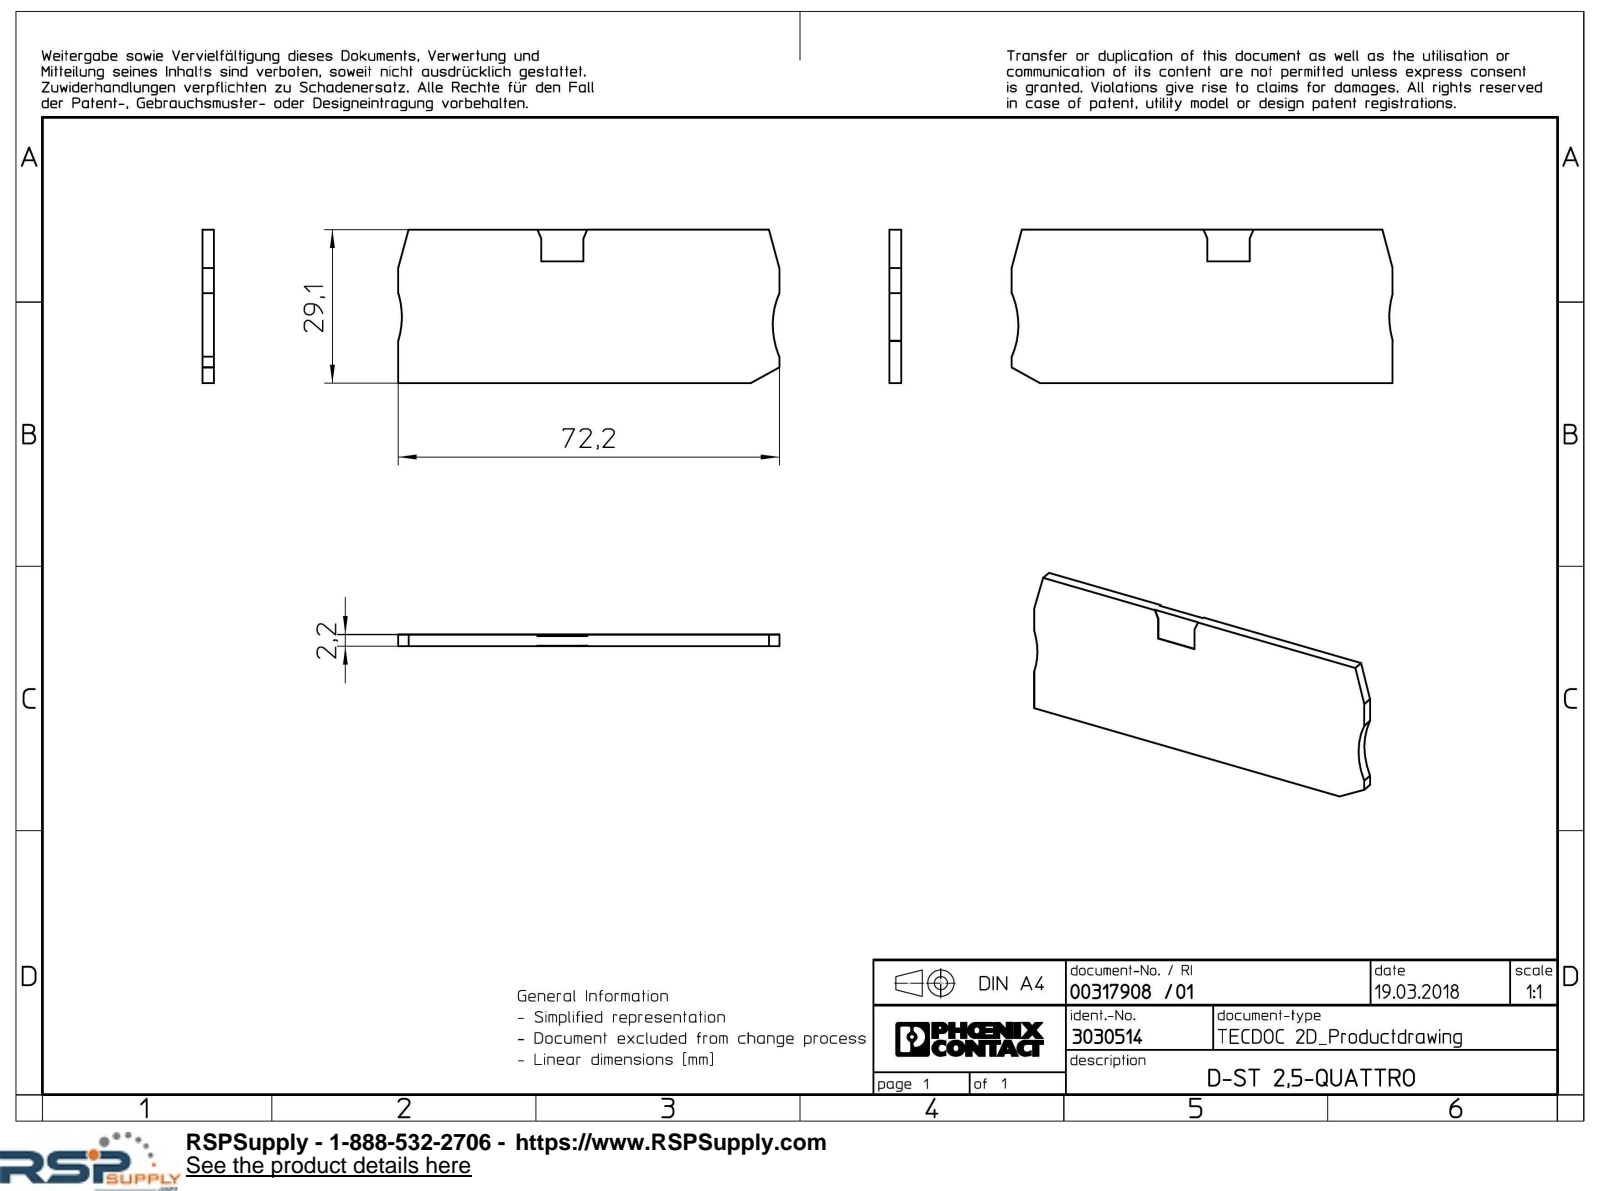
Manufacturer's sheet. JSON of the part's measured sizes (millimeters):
{"part_name": "d-st_25_quattro-select", "step_written_by": "Creo Elements/Direct Modeling 18.1I 14-Aug-2016 (C) Parametric Technology GmbH (AUTOMOTIVE_DESIGN)", "units": "millimeters", "bodies": {"solids": 1, "faces": 25, "planar": 23, "cylindrical": 2, "other": 0}, "overall_size": [72.2, 29.05, 2.2], "volume_mm3": 4514, "surface_area_mm2": 4560, "partial_cylinders_radius": [[15, 2]], "face_to_face_distances": [2.2, 29.05, 1.9, 2.1, 1.8, 72.2, 23.05, 6, 35.1, 37.1]}
